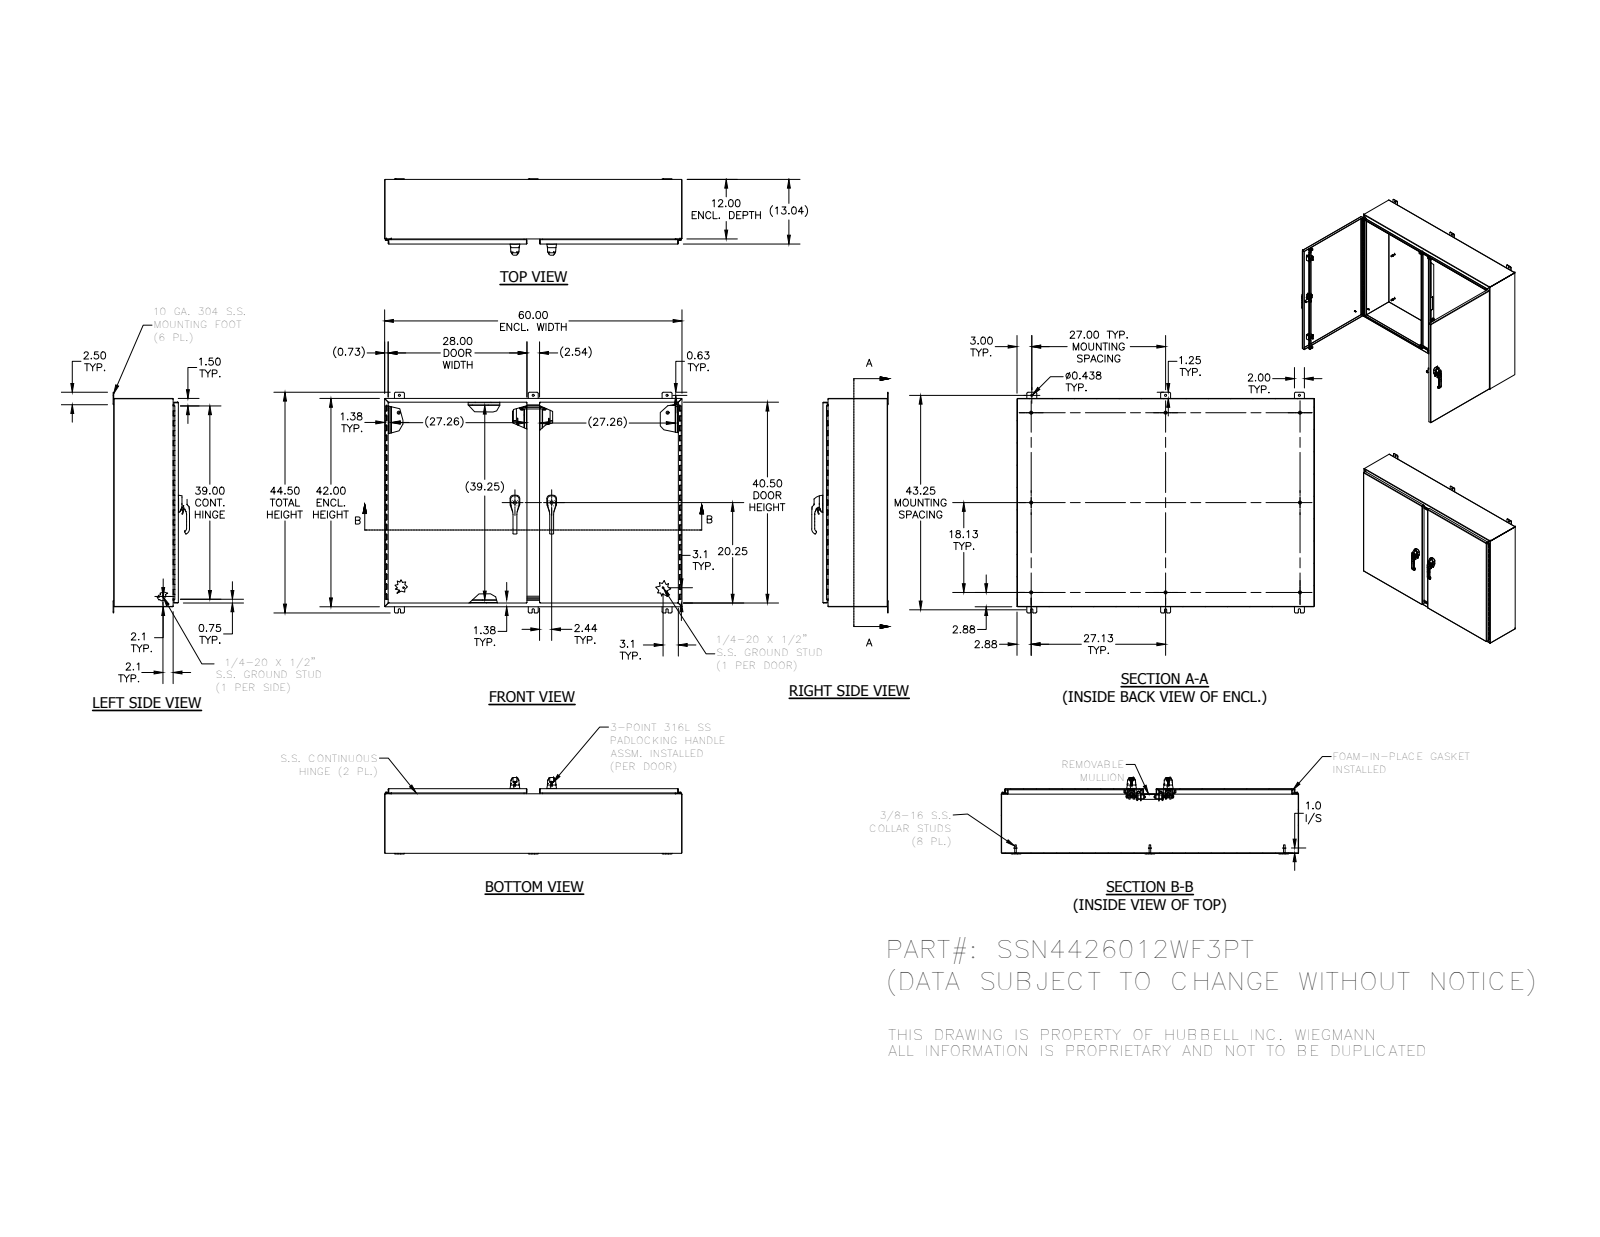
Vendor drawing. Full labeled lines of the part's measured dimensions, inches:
Part name (STEP PRODUCT): SSN44260WF3PTLDR; 1091-903_AF0_2; 1091-76; 1000-277-01 (+8 more)
STEP written by: SolidWorks 2014 (AUTOMOTIVE_DESIGN)
Units: inches
Bodies: 127 solids, 6782 faces (2448 planar, 2814 cylindrical, 1520 other)
Overall size (bounding box): 60 × 44.5 × 15.409
Volume: 718.5 in³ · Surface area: 17 810 in²
Round holes (diameter × count): ⌀0.262 ×12, ⌀0.187 ×8, ⌀0.213 ×6, ⌀0.28 ×6, ⌀0.438 ×6, ⌀0.196 ×4, ⌀0.252 ×4, ⌀0.281 ×4, ⌀0.315 ×4, ⌀0.4 ×4, ⌀0.402 ×4, ⌀0.45 ×4
Round bosses / shafts (diameter × count): ⌀0.25 ×9, ⌀0.625 ×8, ⌀0.33 ×8, ⌀0.533 ×6, ⌀0.236 ×5, ⌀0.531 ×4, ⌀0.438 ×4, ⌀0.435 ×4
Partial cylindrical surfaces — rounded edges, fillets, slot ends (radius × count): R0.02 ×317, R0.012 ×221, R0.019 ×39, R0.031 ×33, R0.125 ×31, R0.05 ×30, R0.25 ×30, R0.079 ×25
Main face-to-face distances: 0.074, 0.094, 12.942, 12.868, 13.035, 12.961, 41.926, 59.926, 11.926, 41.852
Hole centre spacings: 0.38, 0.76, 7.417, 0.492, 0.492, 0.886, 1.236, 1.376
